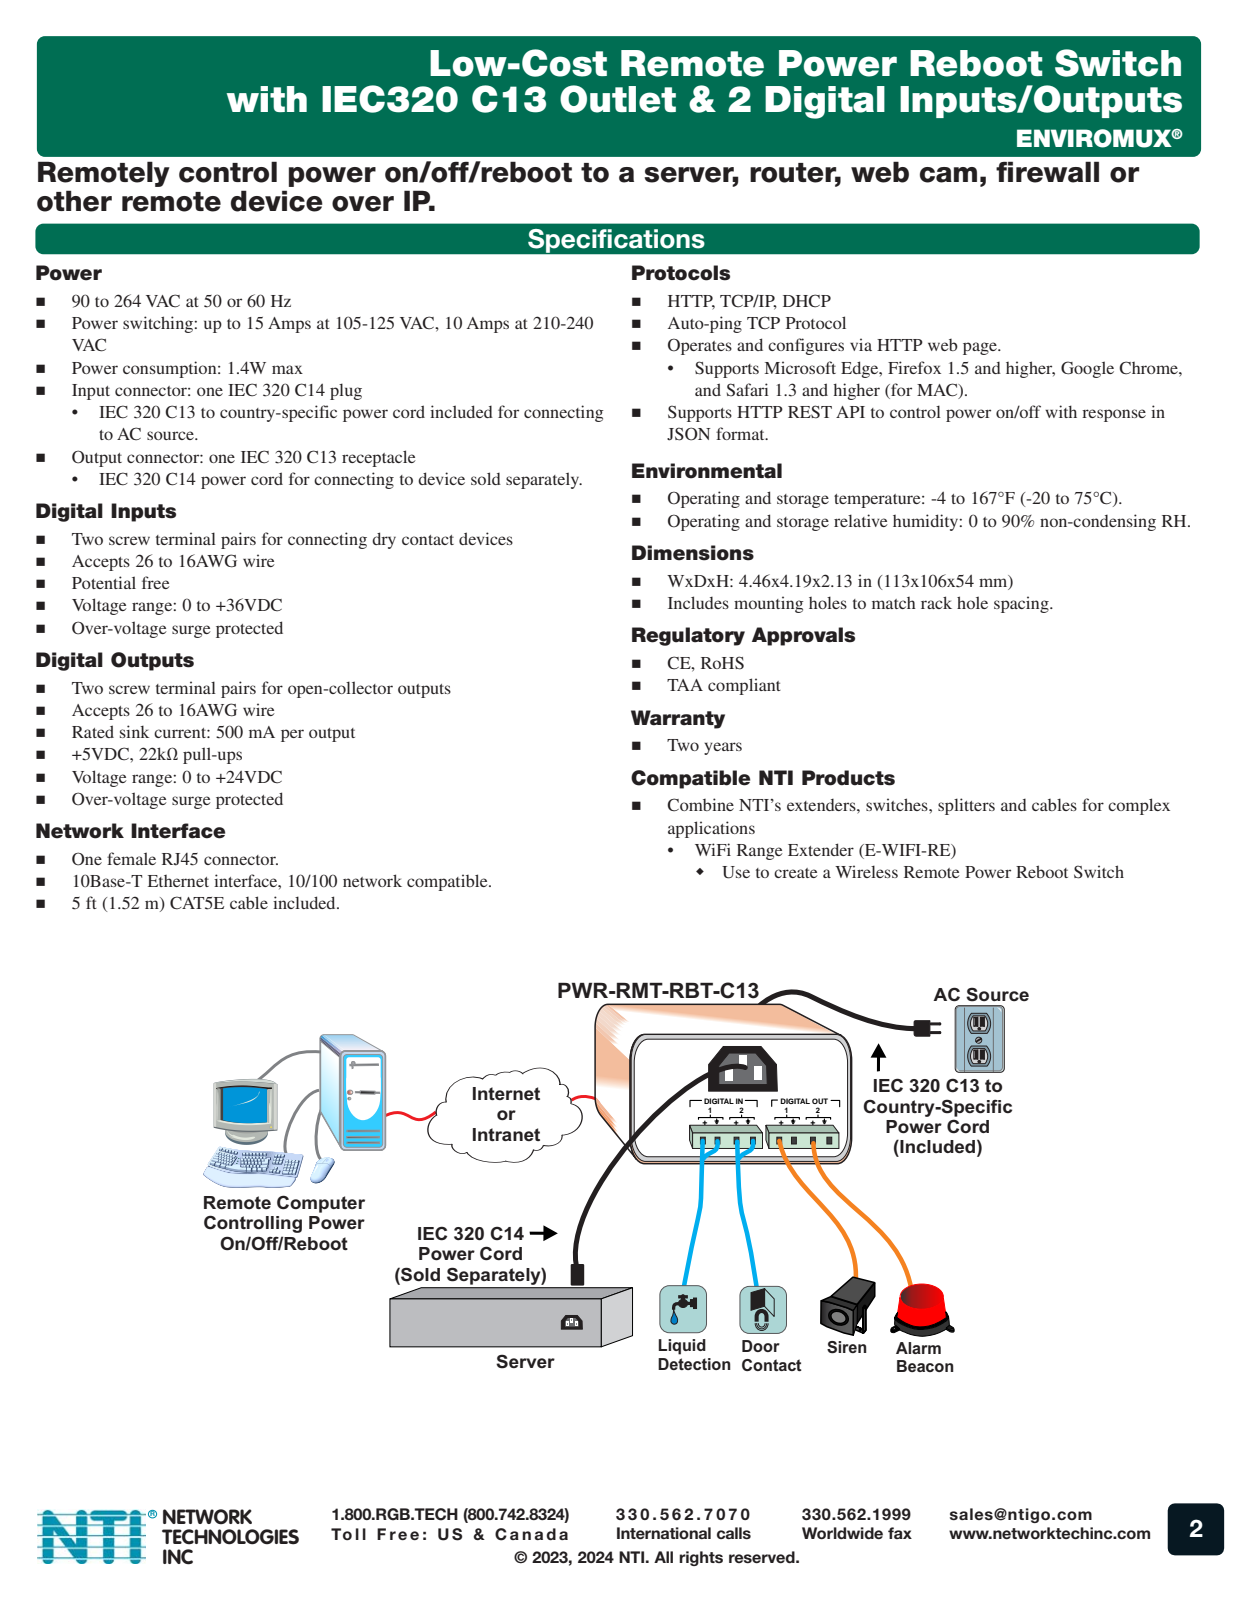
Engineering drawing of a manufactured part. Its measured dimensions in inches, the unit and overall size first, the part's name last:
Units: inches
Overall size (bounding box): 4.452 × 4.391 × 2.128
Round holes (diameter × count): ⌀0.039 ×13, ⌀0.044 ×8, ⌀0.051 ×8, ⌀0.035 ×6, ⌀0.038 ×6, ⌀0.177 ×6, ⌀0.04 ×4, ⌀0.09 ×4, ⌀0.12 ×4, ⌀0.172 ×4, ⌀0.219 ×4, ⌀0.281 ×4
Round bosses / shafts (diameter × count): ⌀0.059 ×8, ⌀0.018 ×8, ⌀0.156 ×4, ⌀0.039 ×4, ⌀0.118 ×2, ⌀0.02 ×2, ⌀0.315 ×1, ⌀0.185 ×1
Partial cylindrical surfaces — rounded edges, fillets, slot ends (radius × count): R0.039 ×57, R0.004 ×53, R0.079 ×29, R0.02 ×21, R0.03 ×16, R0.012 ×8, R0.032 ×8, R0.118 ×8
Main face-to-face distances: 0.189, 0.066, 0.078, 1.861, 1.991, 1.738, 1.927, 1.672, 0.127, 0.062
Hole centre spacings: 0.1, 0.028, 0.146, 0.675, 0.147, 0.154, 0.2, 0.201
Volume: 7.775 in³ · Surface area: 192.2 in²
Bodies: 27 solids, 2201 faces (1432 planar, 621 cylindrical, 148 other)
Part name (STEP PRODUCT): 101223Extruded_5250123L; 101223001CN6656-SS-130250123L; 101223PWR-RMT-RBT-COVER; 101223PWR-RMT-RBT (+7 more)
STEP written by: SolidWorks 2011 (AUTOMOTIVE_DESIGN)
